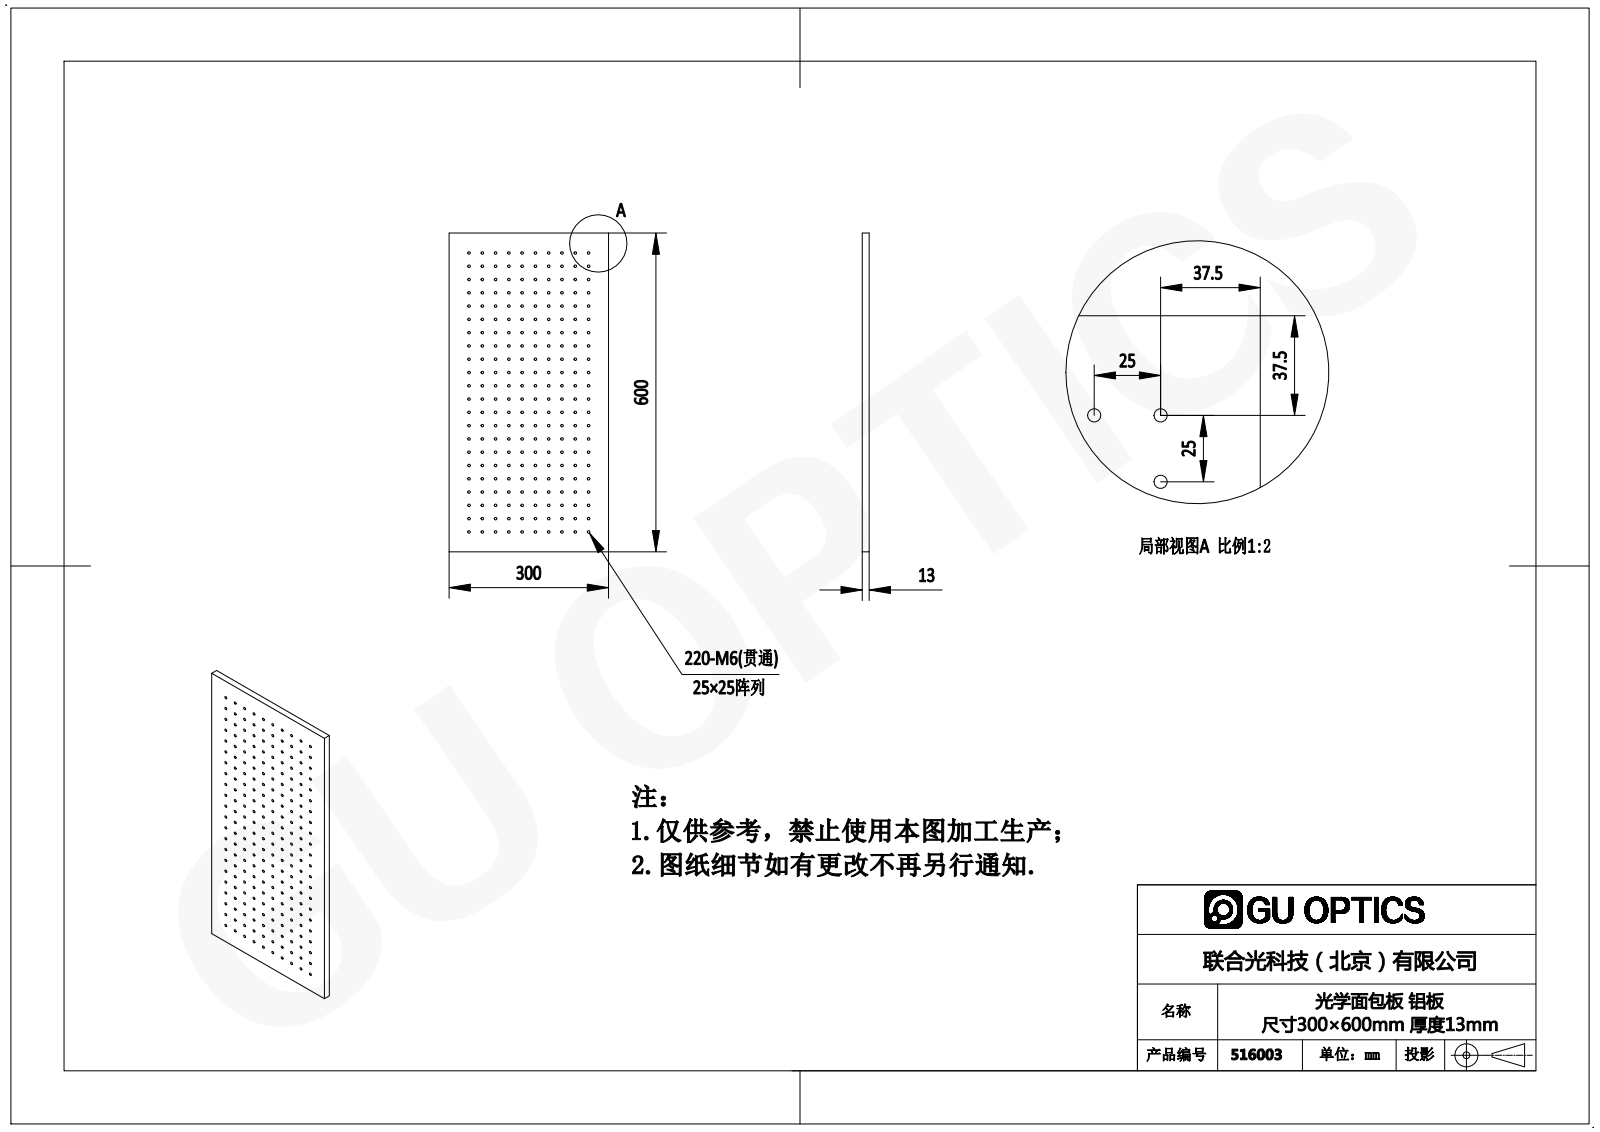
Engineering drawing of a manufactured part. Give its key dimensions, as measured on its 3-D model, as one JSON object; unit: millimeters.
{"part_name": "516003", "step_written_by": "SolidWorks 2016 (AUTOMOTIVE_DESIGN)", "units": "millimeters", "bodies": {"solids": 1, "faces": 446, "planar": 6, "cylindrical": 440, "other": 0}, "overall_size": [600, 300, 13], "volume_mm3": 2284000, "surface_area_mm2": 419685, "round_holes": [[5, 220]], "face_to_face_distances": [13, 300, 600], "hole_center_spacings": [25, 50, 75, 100, 55.9, 125, 35.36, 150]}
